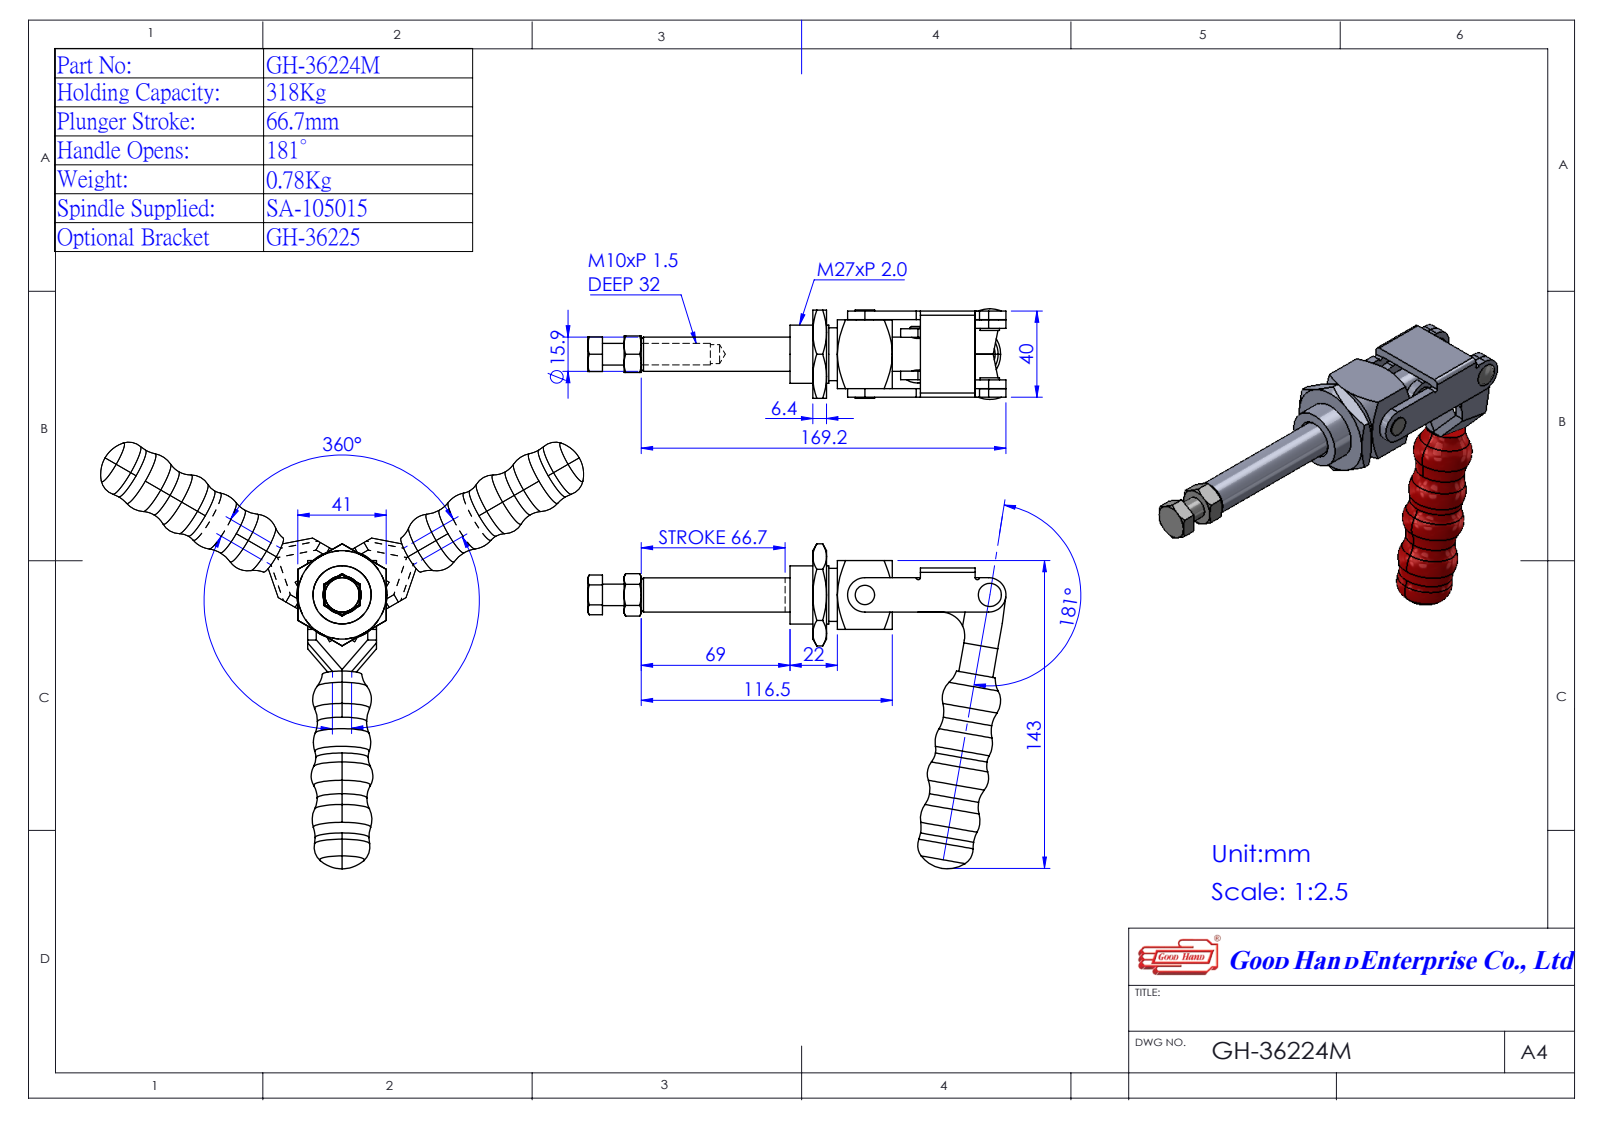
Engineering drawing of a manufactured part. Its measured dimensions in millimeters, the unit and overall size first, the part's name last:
Units: millimetres
Overall size (bounding box): 191.32 × 151.53 × 41.88
Round holes (diameter × count): ⌀6 ×3, ⌀15.9 ×1
Round bosses / shafts (diameter × count): ⌀27 ×1, ⌀16 ×1, ⌀10 ×1, ⌀9 ×1
Partial cylindrical surfaces — rounded edges, fillets, slot ends (radius × count): R8 ×3, R0.5 ×2, R1 ×2, R11 ×1
Main face-to-face distances: 4, 31.9, 35.9, 39.9, 8.1, 27.8, 4.1, 23.8, 27.9, 8
Hole centre spacings: 24.61, 33.4, 58
Volume: 132 421 mm³ · Surface area: 43 196 mm²
Bodies: 4 solids, 198 faces (84 planar, 65 cylindrical, 49 other)
Part name (STEP PRODUCT): Group4^493793(GH-36224M); Group3^493793(GH-36224M); Group2^493793(GH-36224M); Group1^493793(GH-36224M) (+1 more)
STEP written by: SolidWorks 2016 (AUTOMOTIVE_DESIGN)
